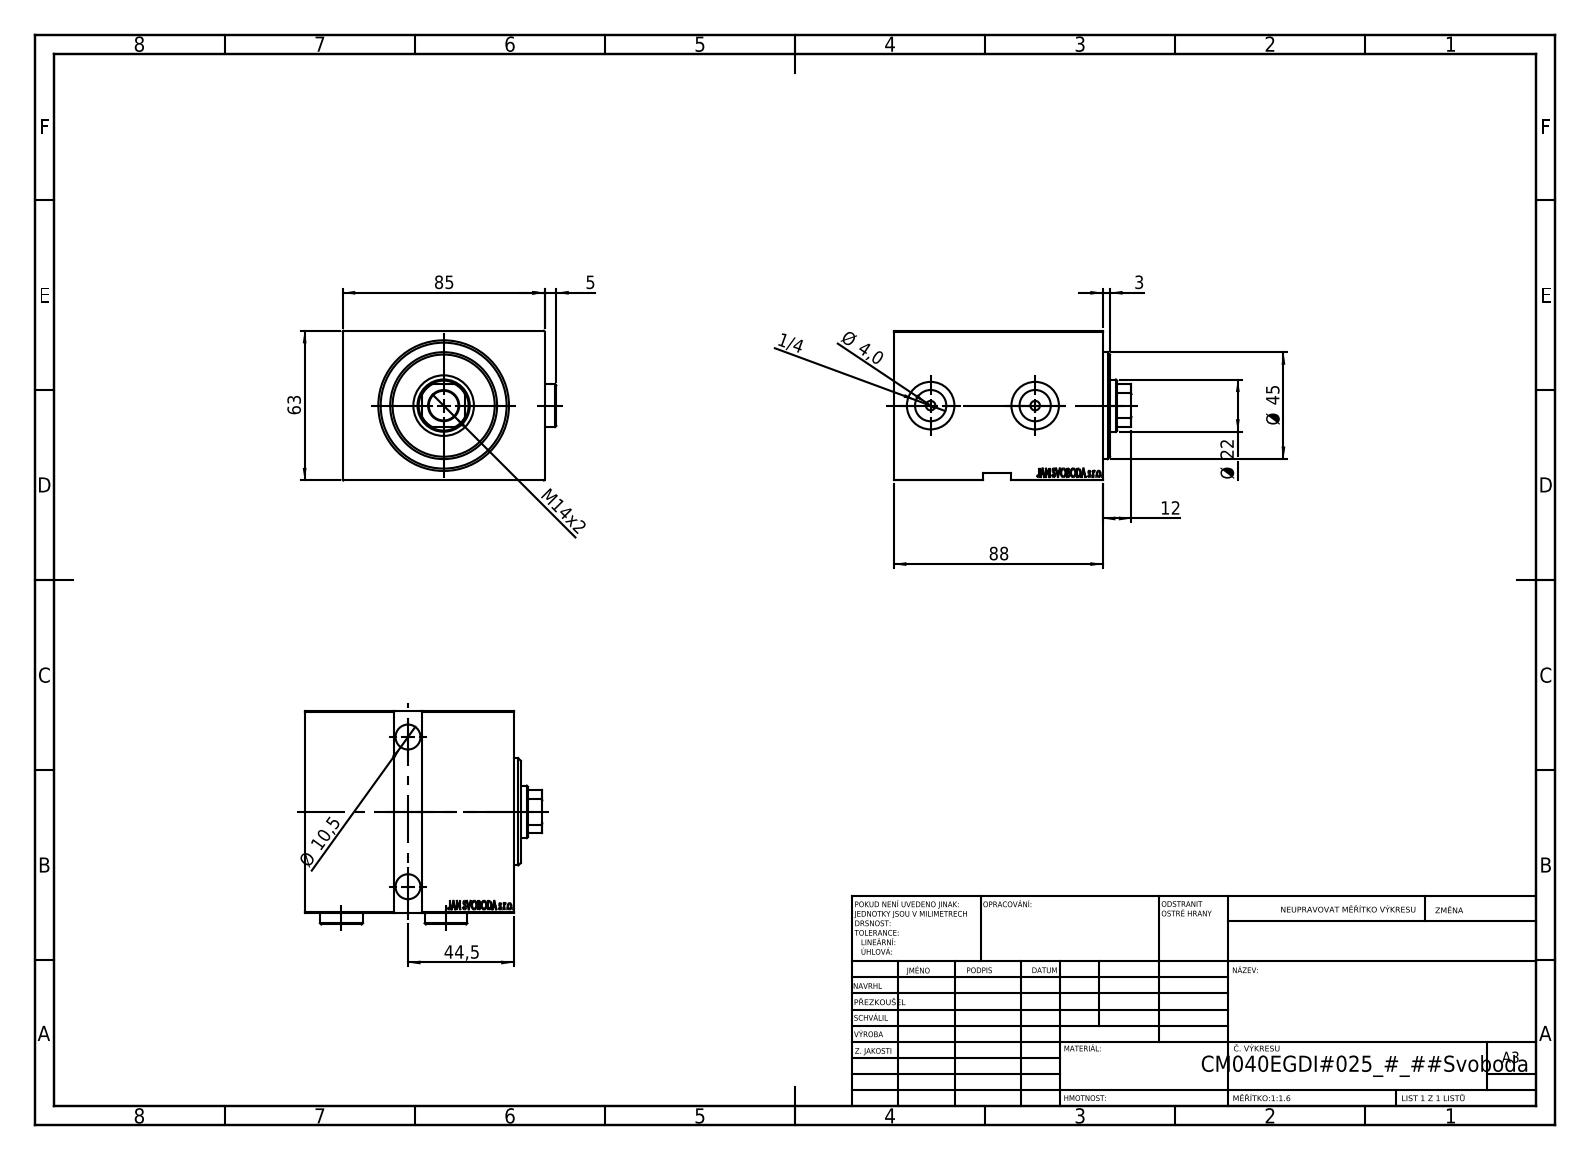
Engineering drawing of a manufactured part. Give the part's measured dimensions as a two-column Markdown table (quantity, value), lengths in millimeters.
| quantity | value |
| --- | --- |
| part name | V450CM_E_VCP; V450CM_E_Body; V450CM_VC_B; Zatka_OIL_PORT |
| STEP written by | SolidWorks 2019 (CONFIG_CONTROL_DESIGN) |
| units | millimeters |
| bodies | 5 solids, 902 faces (444 planar, 60 cylindrical, 398 other) |
| overall size | 100 × 89.9 × 63 |
| volume | 429 983 mm³ |
| surface area | 73 321 mm² |
| round holes (diameter × count) | 4 × 2, 10.5 × 2, 13.16 × 2, 16.5 × 2, 20 × 2, 12.5 × 1, 22 × 1, 25.5 × 1, 40 × 1, 53 × 1 |
| round bosses / shafts (diameter × count) | 18 × 2, 45 × 1, 42 × 1 |
| partial cylindrical surfaces (radius × count) | 10.5 × 1 |
| main face-to-face distances | 63, 85, 88, 5, 12, 76, 3, 71, 83, 84.9 |
| hole center spacings | 44, 63 |
